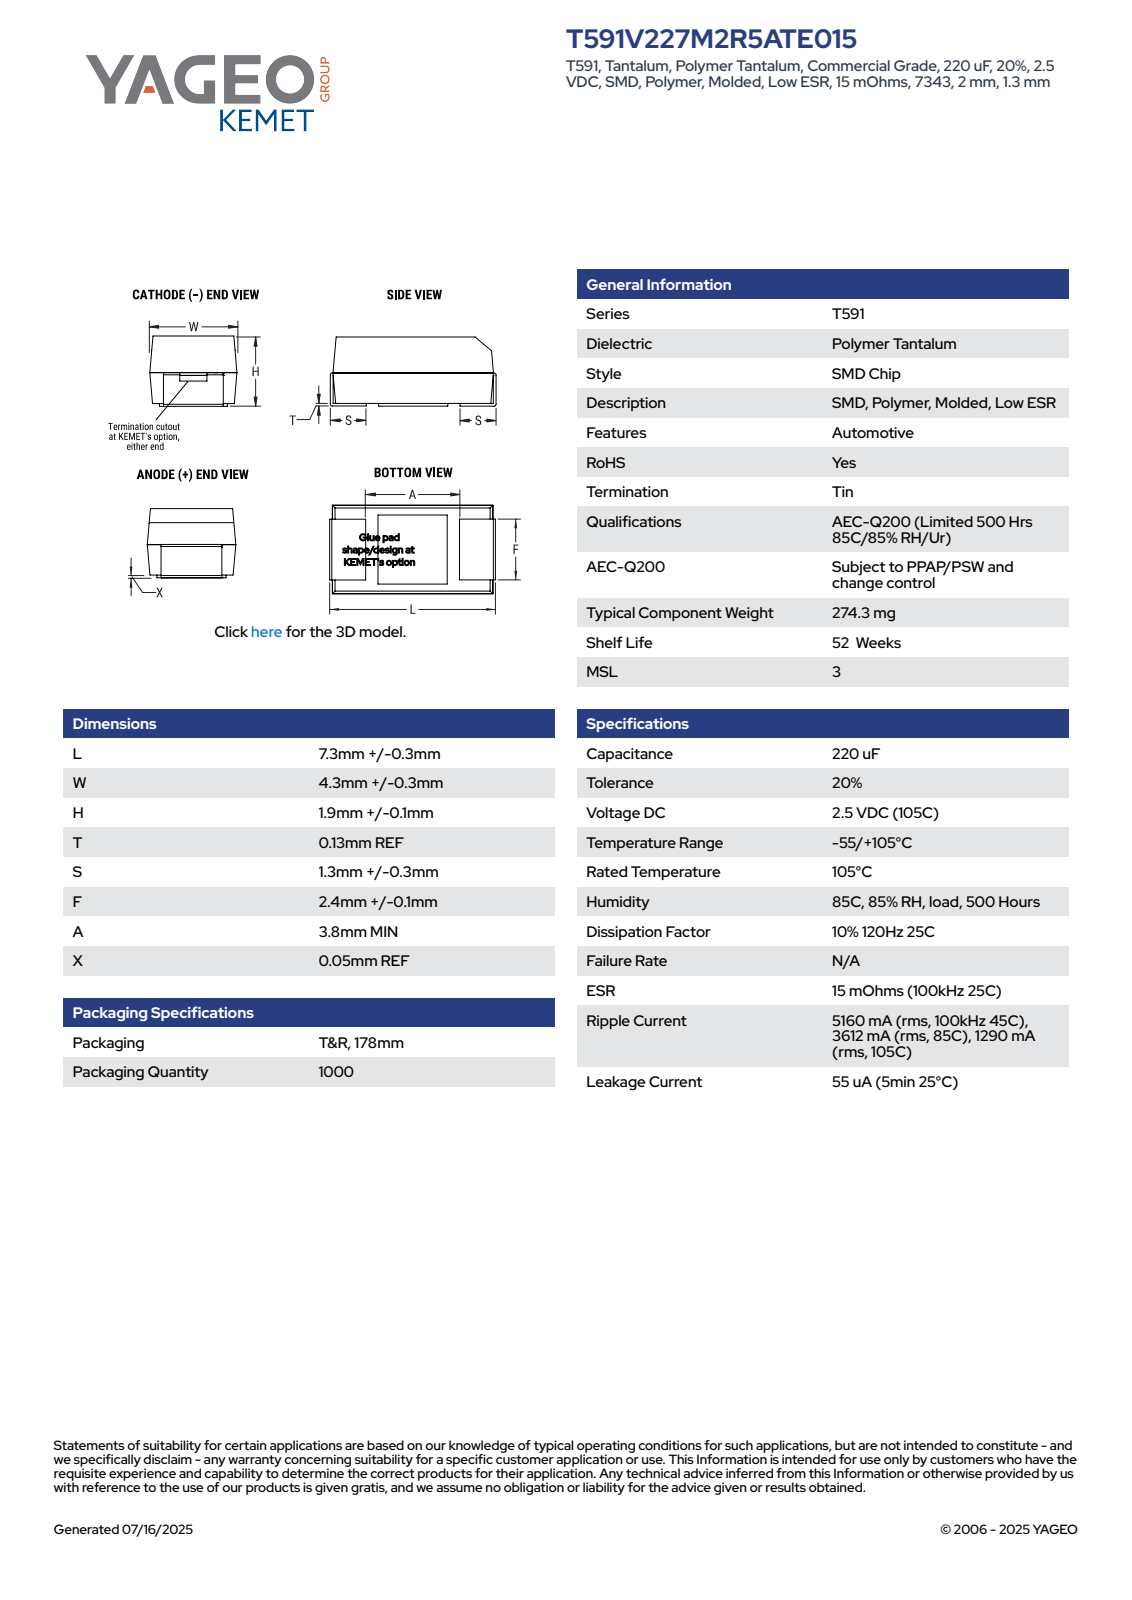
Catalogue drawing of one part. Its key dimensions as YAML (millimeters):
part_name: "CTSM_TCM2NBKRPEG_7343_L7.6W4.6H2T0.13S1.3F2.5A3.8X0.5"
step_written_by: "SolidWorks 2014 (AUTOMOTIVE_DESIGN)"
units: millimeters
bodies: {solids: 4, faces: 90, planar: 86, cylindrical: 4, other: 0}
overall_size: [7.6, 4.6, 2.13]
volume: 62
surface_area: 117
partial_cylinders:
  - {radius: 0.1, count: 4}
face_to_face_distances: [2, 4.45, 4.44, 2.13, 7.47, 7.6, 7.34, 1.3, 6.3, 1.17]
